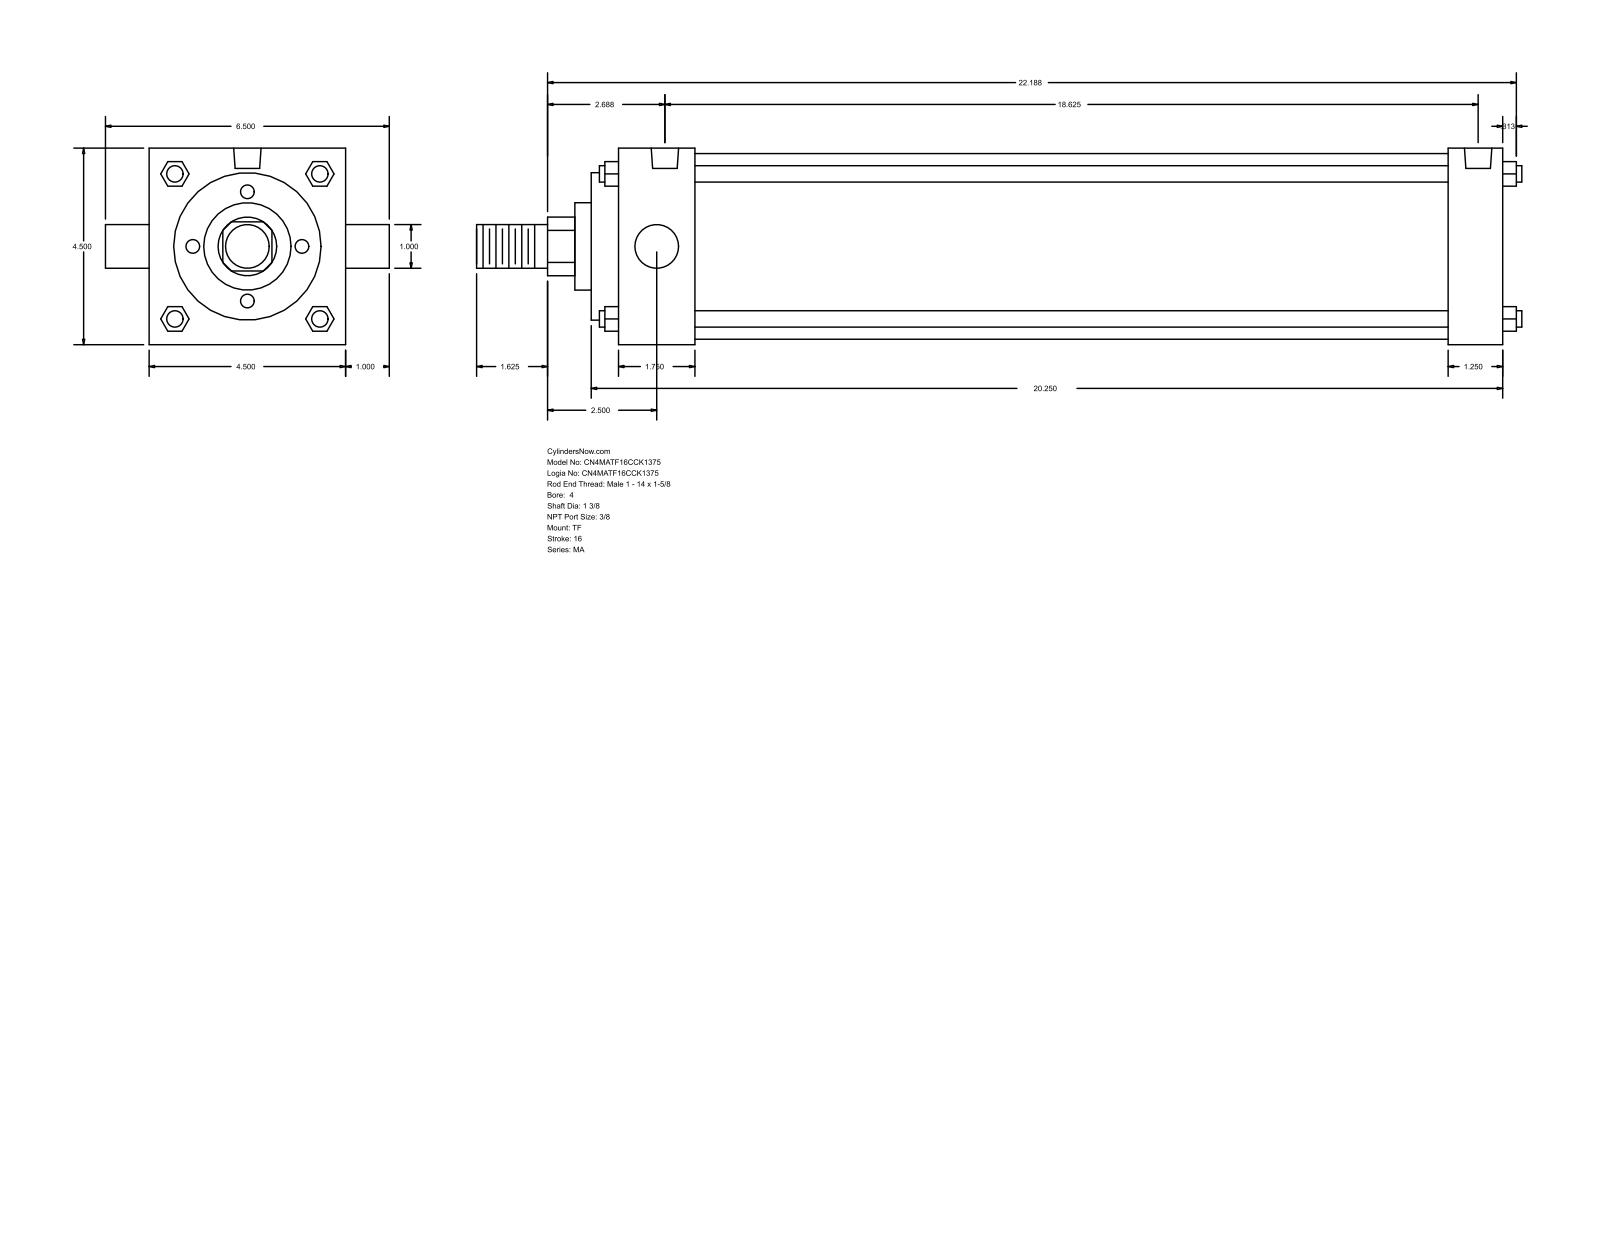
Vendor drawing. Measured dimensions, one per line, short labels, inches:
name: MA_TF__0400_1.375
written by: GSSL Pune (CONFIG_CONTROL_DESIGN)
unit: in
bodies: 0 solids, 122 faces (93 planar, 29 cylindrical, 0 other)
size: 23.937 × 6.5 × 4.5
holes: 3× ⌀0.437, 2× ⌀0.627
bosses: 4× ⌀0.375, 2× ⌀1, 1× ⌀4.25, 1× ⌀3.375, 1× ⌀2, 1× ⌀1.375
rounds: 1× R0.672
face distances: 4.5, 20.25, 20.875, 0.625, 19.625, 19, 1.25, 2.375, 1.75, 17.25
hole spacings: 0.187, 0.188, 18.25, 18.437, 18.438, 18.625
